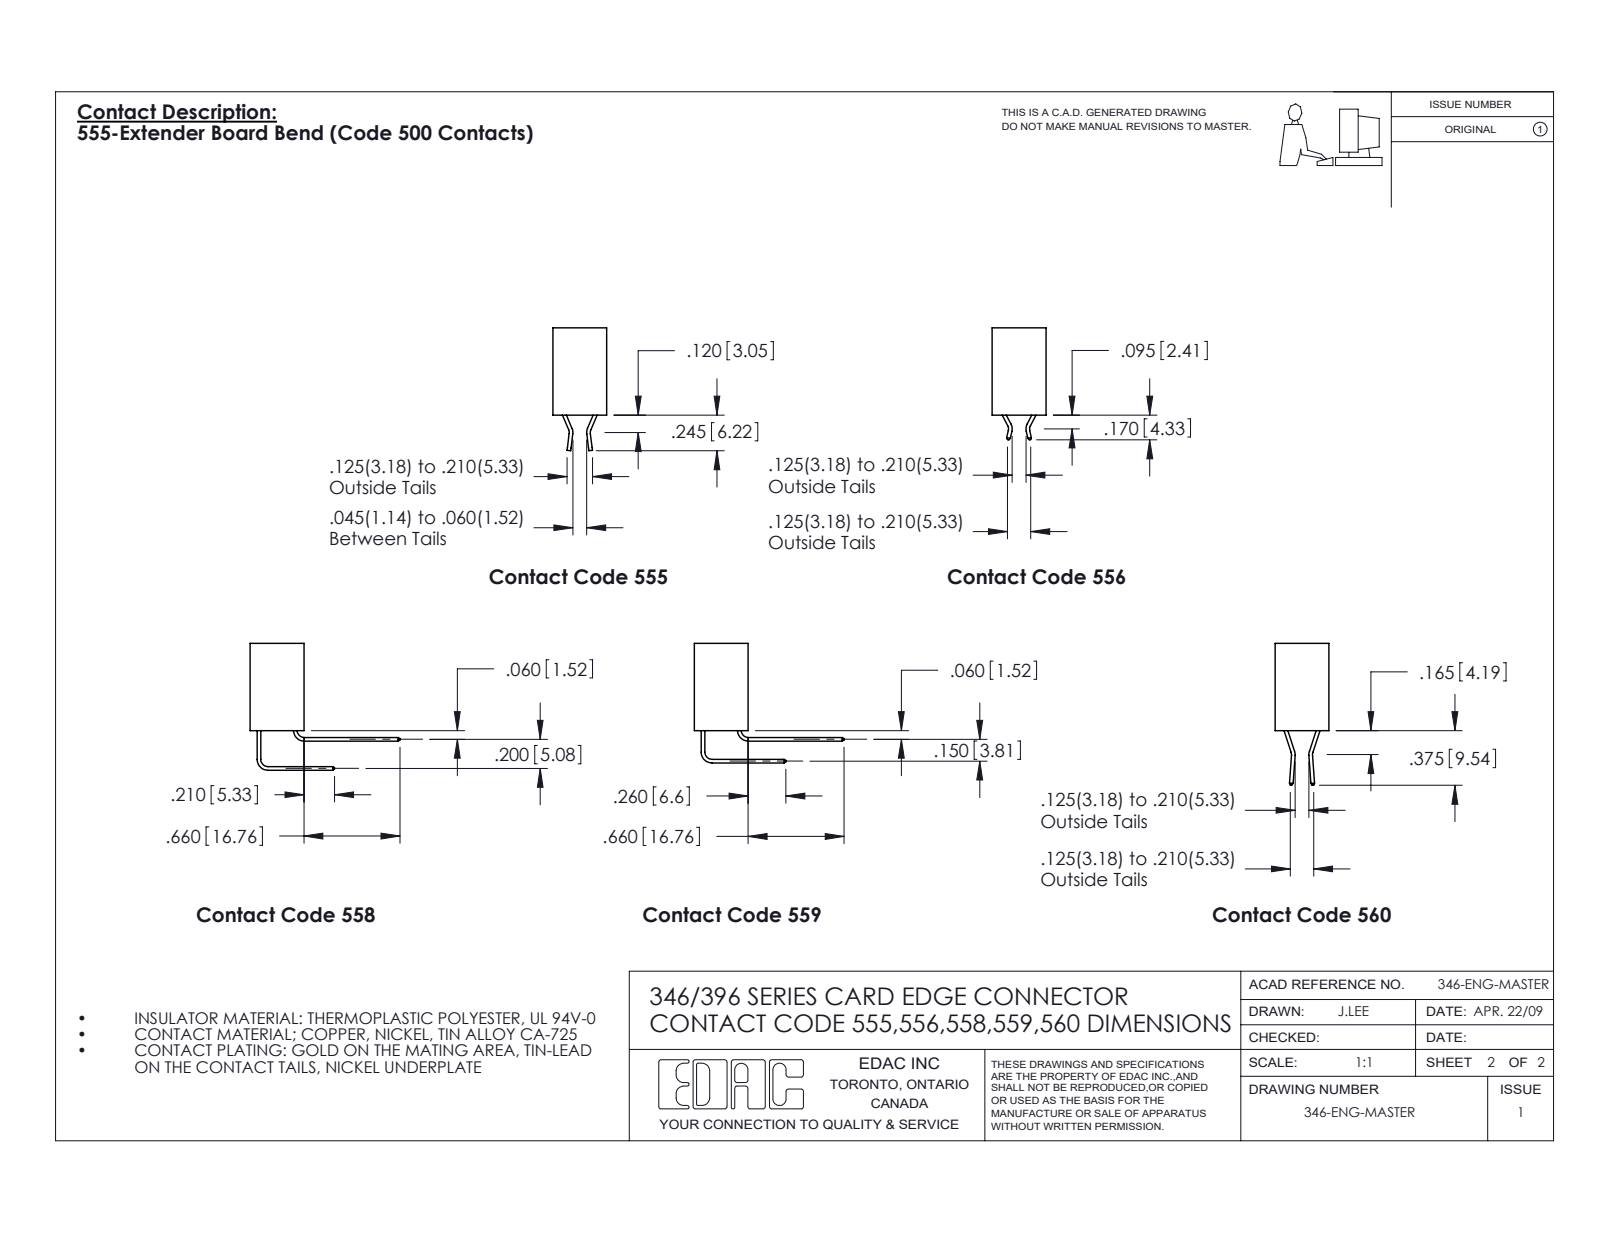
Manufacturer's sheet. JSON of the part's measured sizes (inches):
{"part_name": "345-292-001_345-293-140; 346 Part_No Mounting Lugs; 396-023-540-101", "step_written_by": "SolidWorks 2016 (CONFIG_CONTROL_DESIGN)", "units": "inches", "bodies": {"solids": 24, "faces": 1448, "planar": 992, "cylindrical": 456, "other": 0}, "overall_size": [3.16, 1.16, 0.37], "volume_in3": 0.496, "surface_area_in2": 15.91, "round_holes": [[0.064, 1]], "partial_cylinders_radius": [[0.006, 46], [0.01, 46], [0.01, 22], [0.007, 6], [0.031, 6], [0.026, 3], [0.031, 2], [0.04, 2]], "face_to_face_distances": [0.048, 0.322, 0.25, 0.37, 0.072, 0.298, 0.025, 0.148, 0.222, 0.1]}
